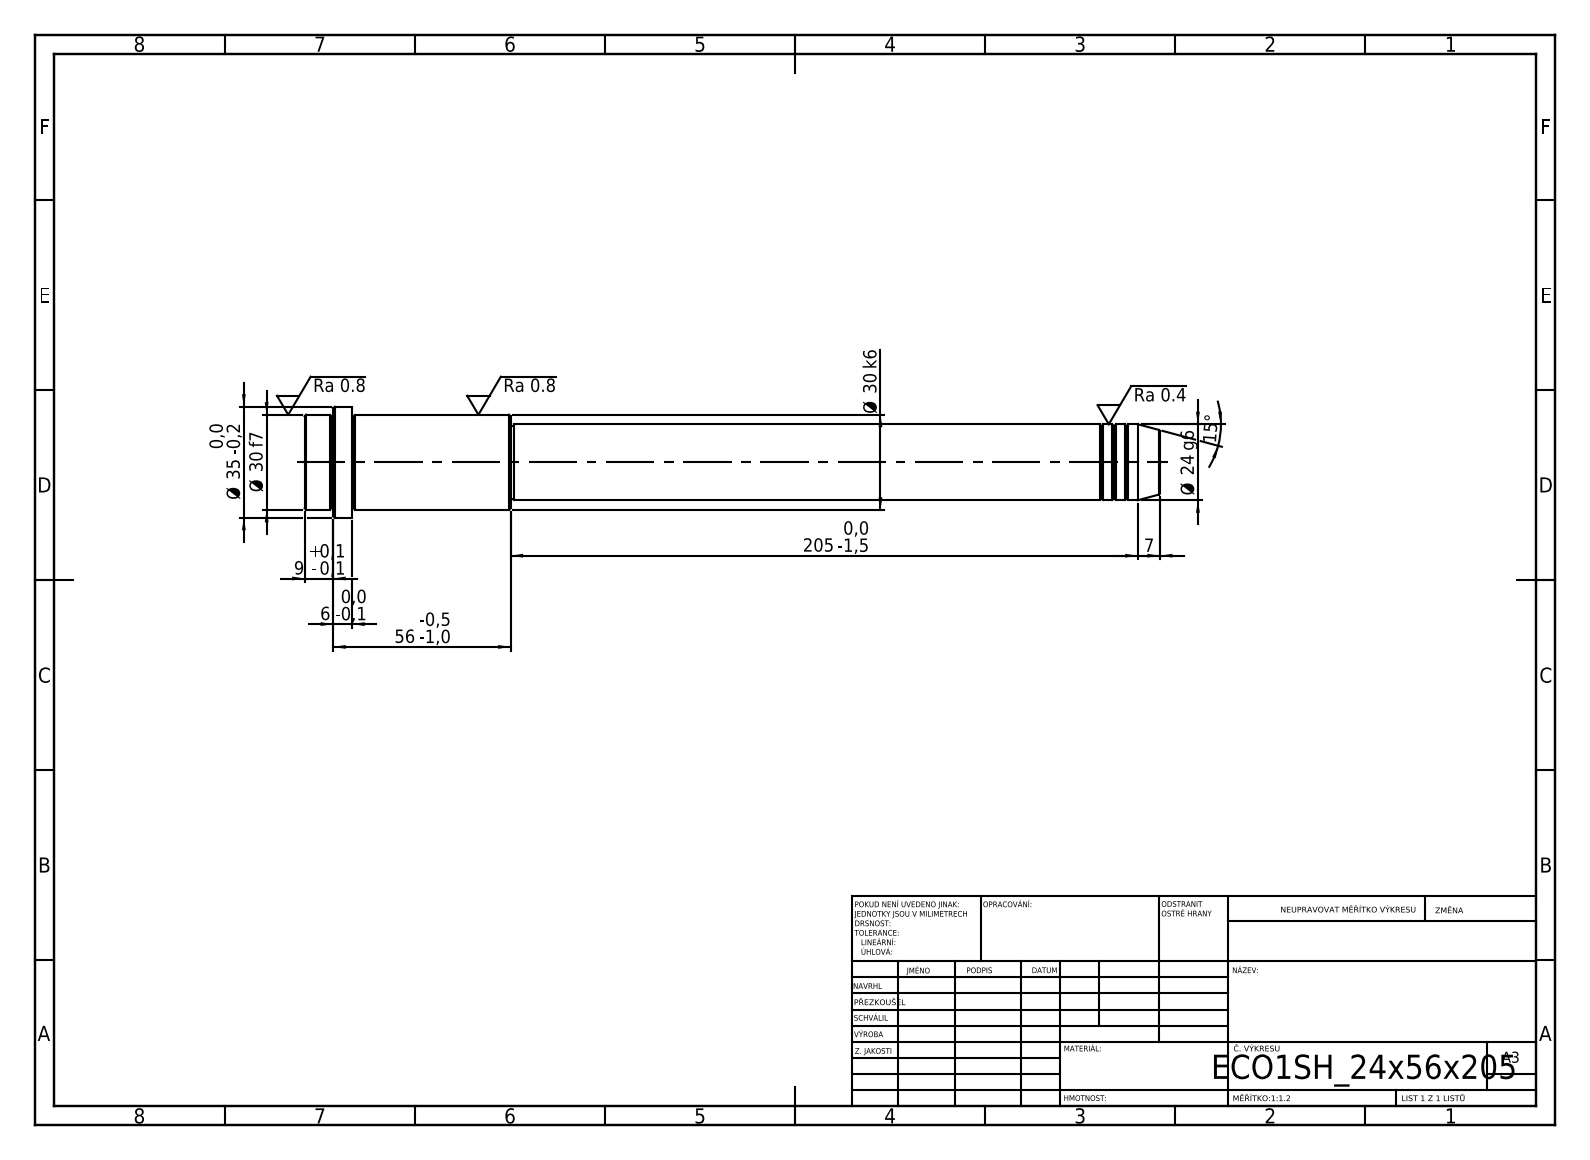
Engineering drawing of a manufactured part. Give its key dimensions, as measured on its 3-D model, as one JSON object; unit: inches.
{"step_written_by": "SolidWorks 2019 (CONFIG_CONTROL_DESIGN)", "units": "inches", "bodies": {"solids": 1, "faces": 52, "planar": 6, "cylindrical": 16, "other": 30}, "overall_size": [10.63, 1.378, 1.378], "volume_in3": 8.514, "surface_area_in2": 36.65, "round_bosses_or_shafts": [[1.378, 1], [1.181, 1], [0.945, 1], [0.906, 1]], "face_to_face_distances": [10.63, 10.039, 0.591, 8.071, 1.969, 2.559, 10.276, 2.205, 0.236, 0.354]}
